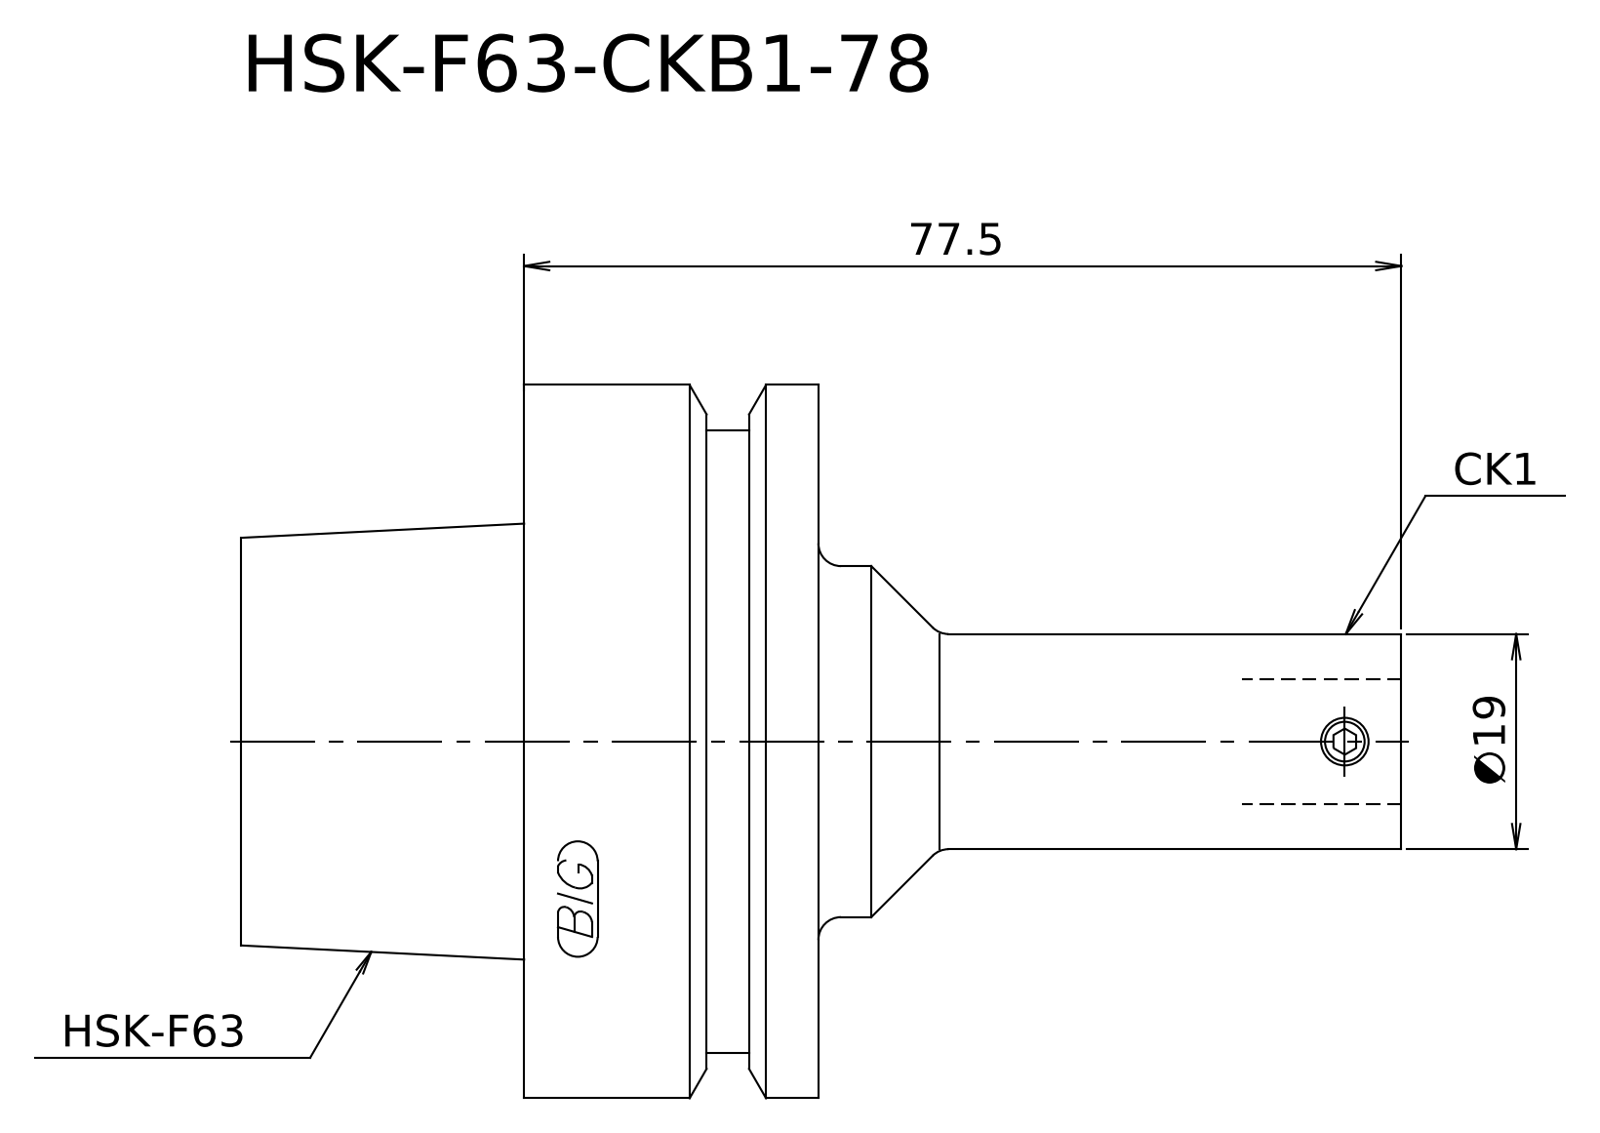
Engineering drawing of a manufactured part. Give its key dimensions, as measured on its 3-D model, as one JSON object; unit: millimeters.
{"step_written_by": "Kubotek KeyCreator V8.5.1 (14335) (CONFIG_CONTROL_DESIGN)", "units": "millimeters", "bodies": {"solids": 1, "faces": 18, "planar": 6, "cylindrical": 6, "other": 6}, "overall_size": [102.5, 63, 63], "volume_mm3": 123080, "surface_area_mm2": 18093, "round_bosses_or_shafts": [[63, 1], [55, 1], [38.3, 1], [31, 1], [19, 1]], "face_to_face_distances": [26, 51, 25, 51.5, 77.5, 102.5, 57.62, 6.12, 19.88, 44.88]}
